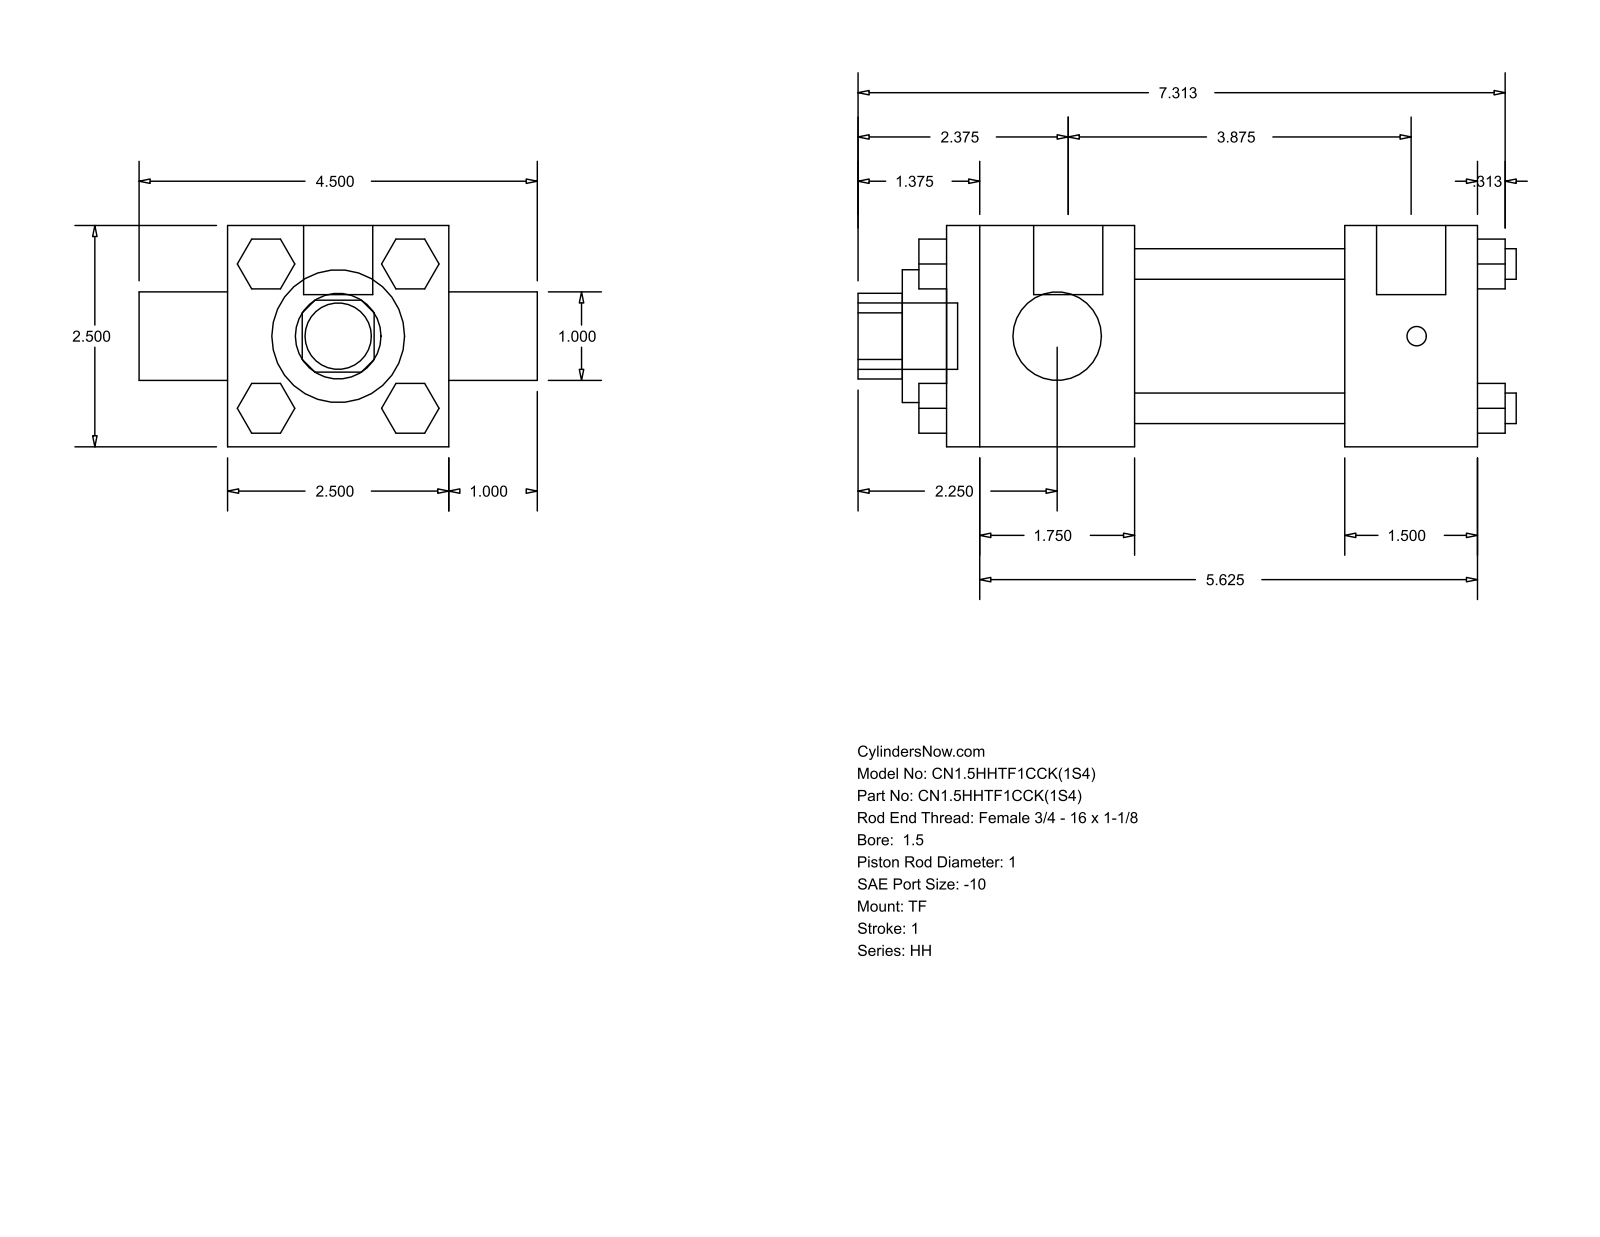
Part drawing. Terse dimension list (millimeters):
name: HH_TF__0150_1
written by: GSSL Pune (CONFIG_CONTROL_DESIGN)
unit: mm
bodies: 0 solids, 120 faces (92 planar, 28 cylindrical, 0 other)
size: 188.91 × 114.3 × 63.5
holes: 2× ⌀25.4, 1× ⌀38.1, 1× ⌀44.45
bosses: 4× ⌀8.76, 3× ⌀5.56, 2× ⌀19.84, 1× ⌀19.05
rounds: 1× R12.29
face distances: 63.5, 114.3, 98.42, 60.32, 38.1, 53.98, 152.4, 160.34, 25.4, 20.7
